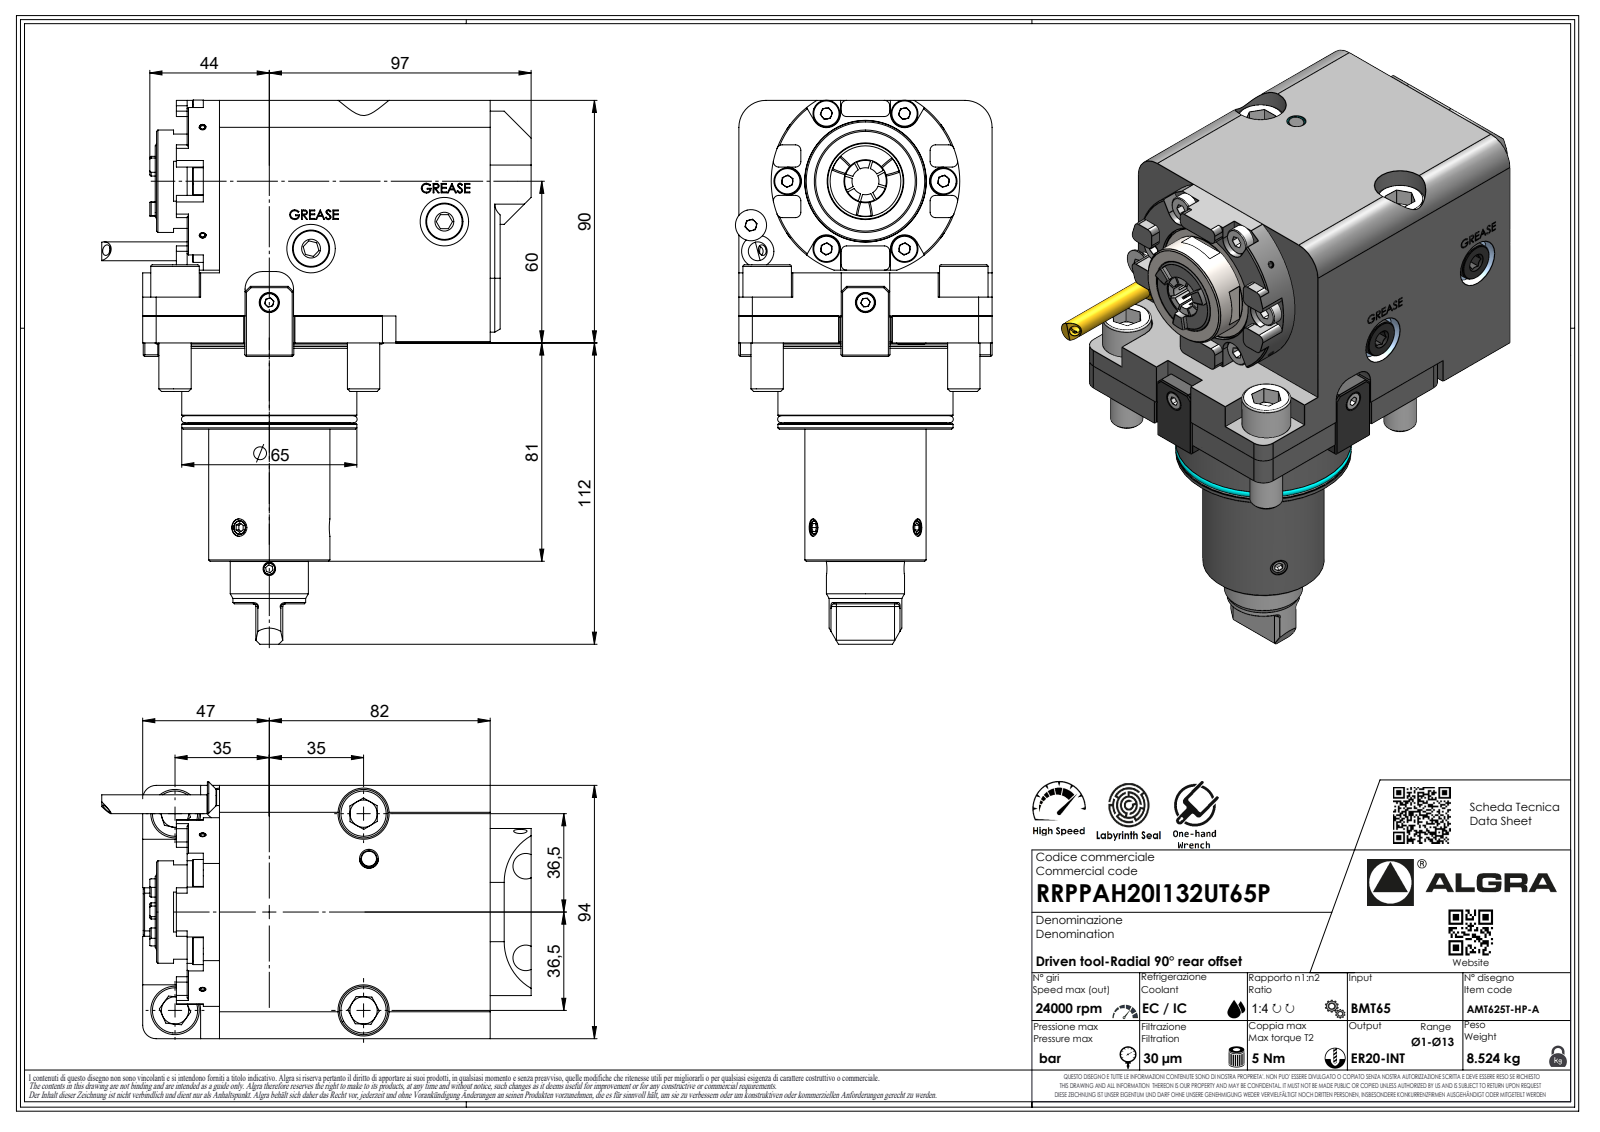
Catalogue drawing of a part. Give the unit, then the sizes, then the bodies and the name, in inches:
Units: inches
Overall size (bounding box): 7.945 × 6.276 × 3.701
Round holes (diameter × count): ⌀0.374 ×4, ⌀0.083 ×1, ⌀0.157 ×1, ⌀0.63 ×1, ⌀1.78 ×1
Round bosses / shafts (diameter × count): ⌀0.472 ×4, ⌀1.772 ×2, ⌀0.709 ×2, ⌀2.559 ×1, ⌀2.543 ×1, ⌀2.37 ×1, ⌀1.496 ×1, ⌀1.142 ×1
Partial cylindrical surfaces — rounded edges, fillets, slot ends (radius × count): R0.079 ×25, R0.013 ×7, R0.02 ×7, R0.146 ×7, R0.039 ×6, R0.207 ×6, R1.281 ×5, R0.787 ×4
Main face-to-face distances: 3.701, 3.543, 0.146, 3.957, 4.102, 1.26, 0.472, 2.283, 2.52, 1.024
Hole centre spacings: 0.952, 0.975, 1.031, 1.868, 1.339, 1.811
Volume: 74.02 in³ · Surface area: 145 in²
Bodies: 1 solid, 676 faces (423 planar, 112 cylindrical, 141 other)
Part name (STEP PRODUCT): RRPPAH20I132UT65P
STEP written by: SolidWorks 2023 (AUTOMOTIVE_DESIGN)
